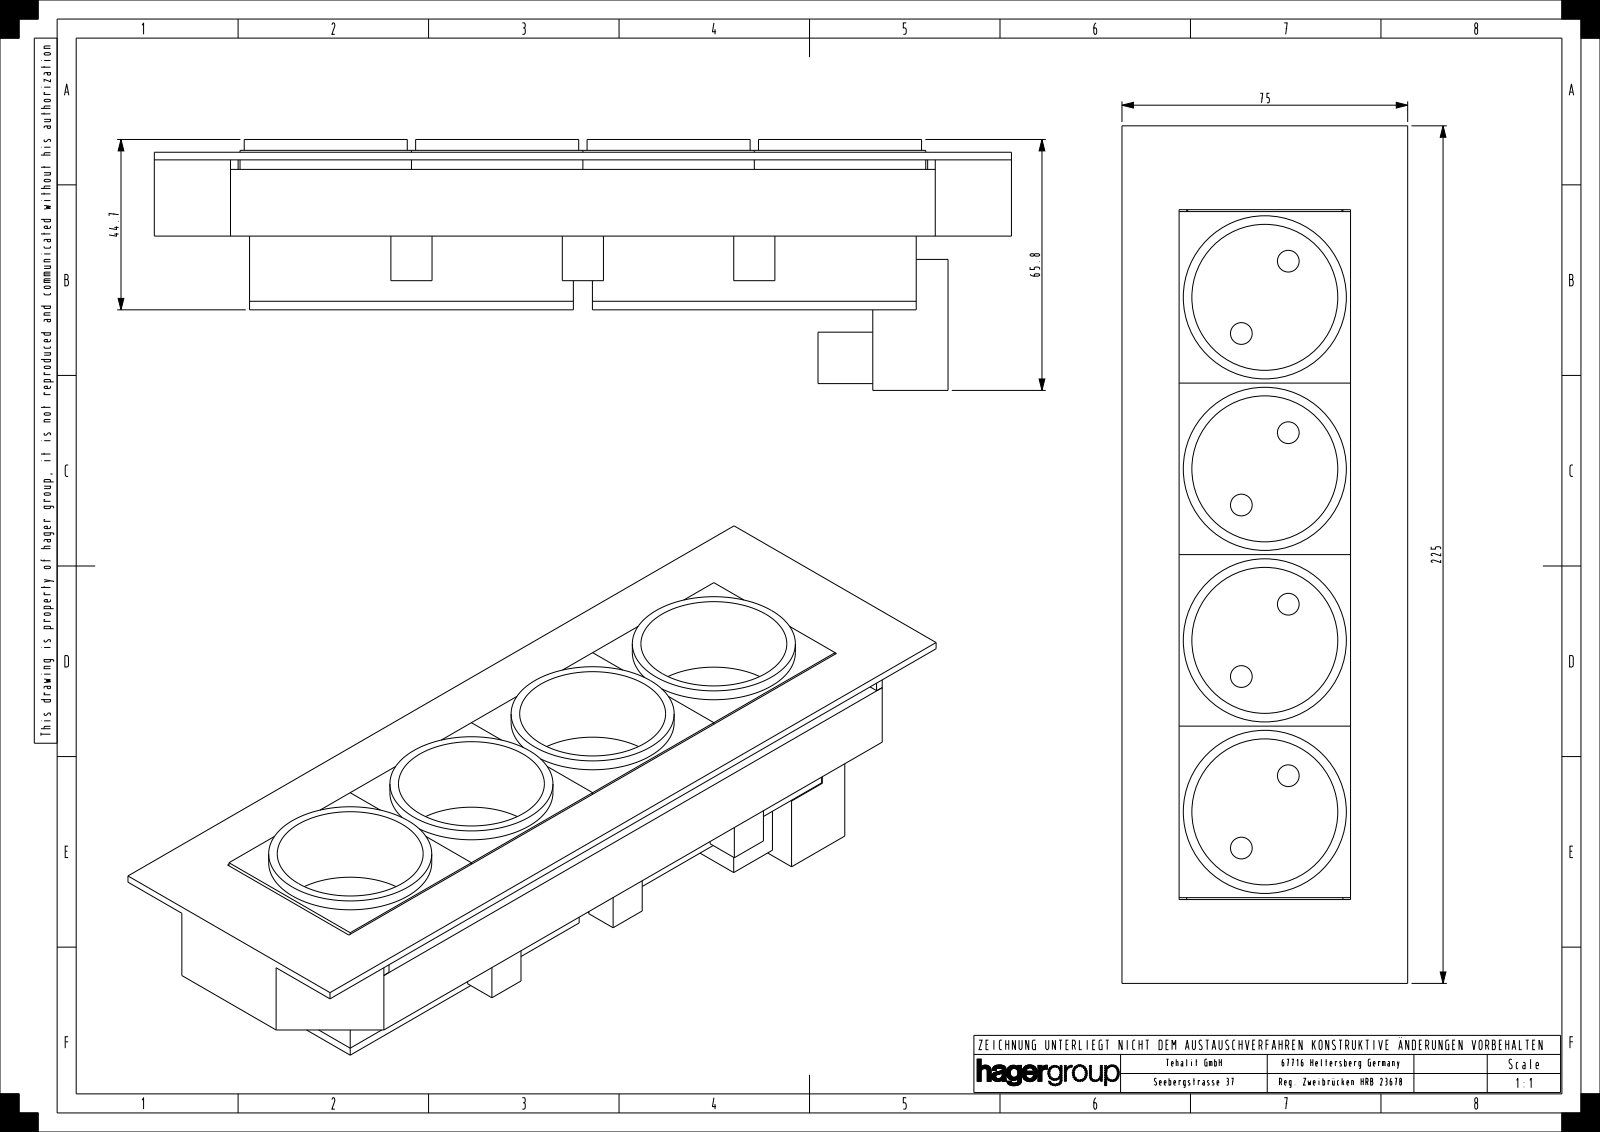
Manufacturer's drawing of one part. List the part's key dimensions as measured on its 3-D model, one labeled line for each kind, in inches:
Part name (STEP PRODUCT): GTVR400_1; SOCKEL-2-FACH-VEREINFACHT_8; ABDECKUNG-SIMPLIFIED_9; ESR2339010-VEREINFACHT_ASM_7_AF0_ASM (+5 more)
STEP written by: CREO PARAMETRIC BY PTC INC, 2022281 (AUTOMOTIVE_DESIGN)
Units: inches
Bodies: 8 solids, 188 faces (148 planar, 40 cylindrical, 0 other)
Overall size (bounding box): 8.858 × 2.953 × 2.592
Volume: 16.62 in³ · Surface area: 224 in²
Round holes (diameter × count): ⌀0.224 ×8, ⌀1.508 ×4
Round bosses / shafts (diameter × count): ⌀1.685 ×4, ⌀1.516 ×4
Main face-to-face distances: 0.098, 0.031, 0.689, 0.079, 1.543, 0.866, 1.673, 1.642, 0.787, 0.762
Hole centre spacings: 1.772, 0.445, 1.419, 2.159, 3.543, 0.891, 3.179, 3.924
